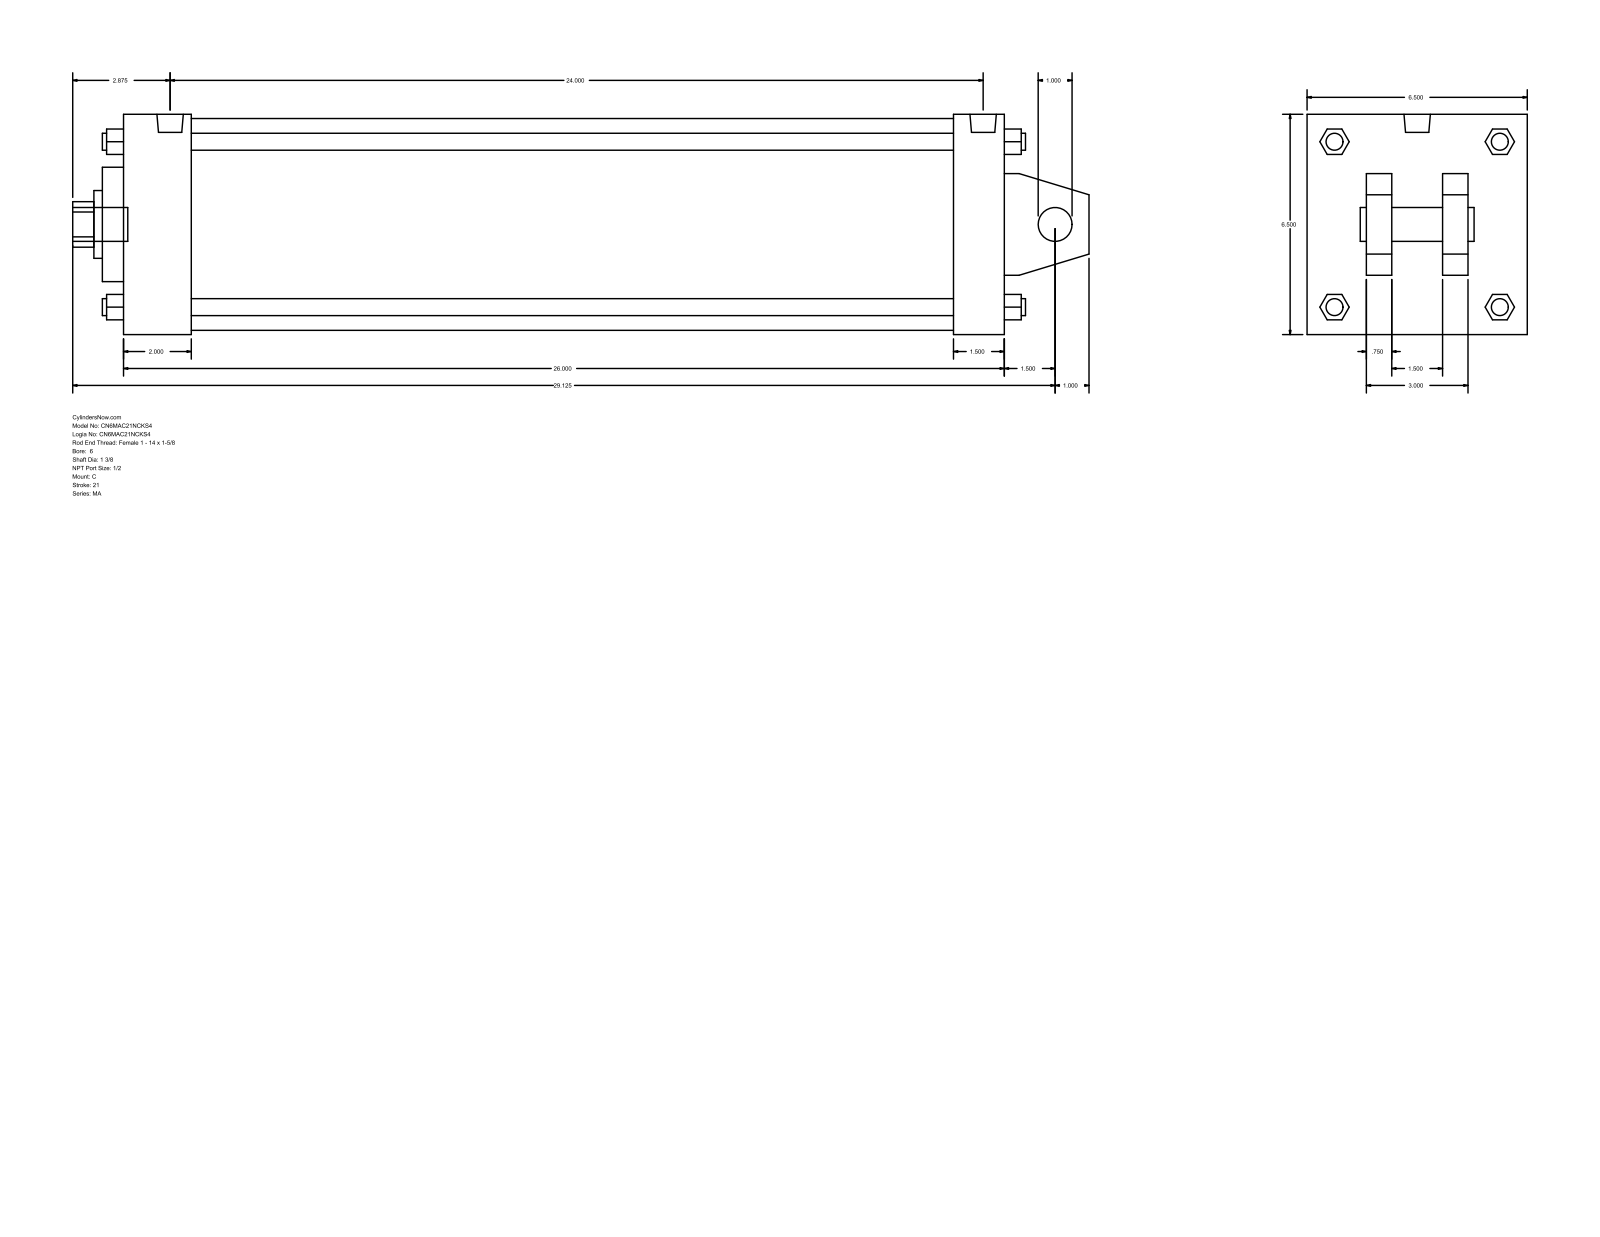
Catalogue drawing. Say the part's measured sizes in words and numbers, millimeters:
The part is named "MA_C__0600_1.375". Its 3-D file was written by "GSSL Pune (CONFIG_CONTROL_DESIGN)". It is 0 solids with 141 faces: 109 planar, 32 cylindrical and 0 other. Overall it measures 762 by 165.1 by 165.1 millimeters. Round holes: 1 of diameter 25.4, 1 of diameter 34.92, 1 of diameter 50.8, 1 of diameter 85.72, 1 of diameter 158.75. Round bosses or shafts: 4 of diameter 17.46, 4 of diameter 12.7, 2 of diameter 19.77, 1 of diameter 25.4. Partial cylindrical surfaces (rounded edges, fillets, slot ends): 1 of radius 17.06. The main face-to-face distances are 165.1, 660.4, 38.1, 19.05, 63.5, 101.6, 50.8, 44.45, 120.65, 622.3.
